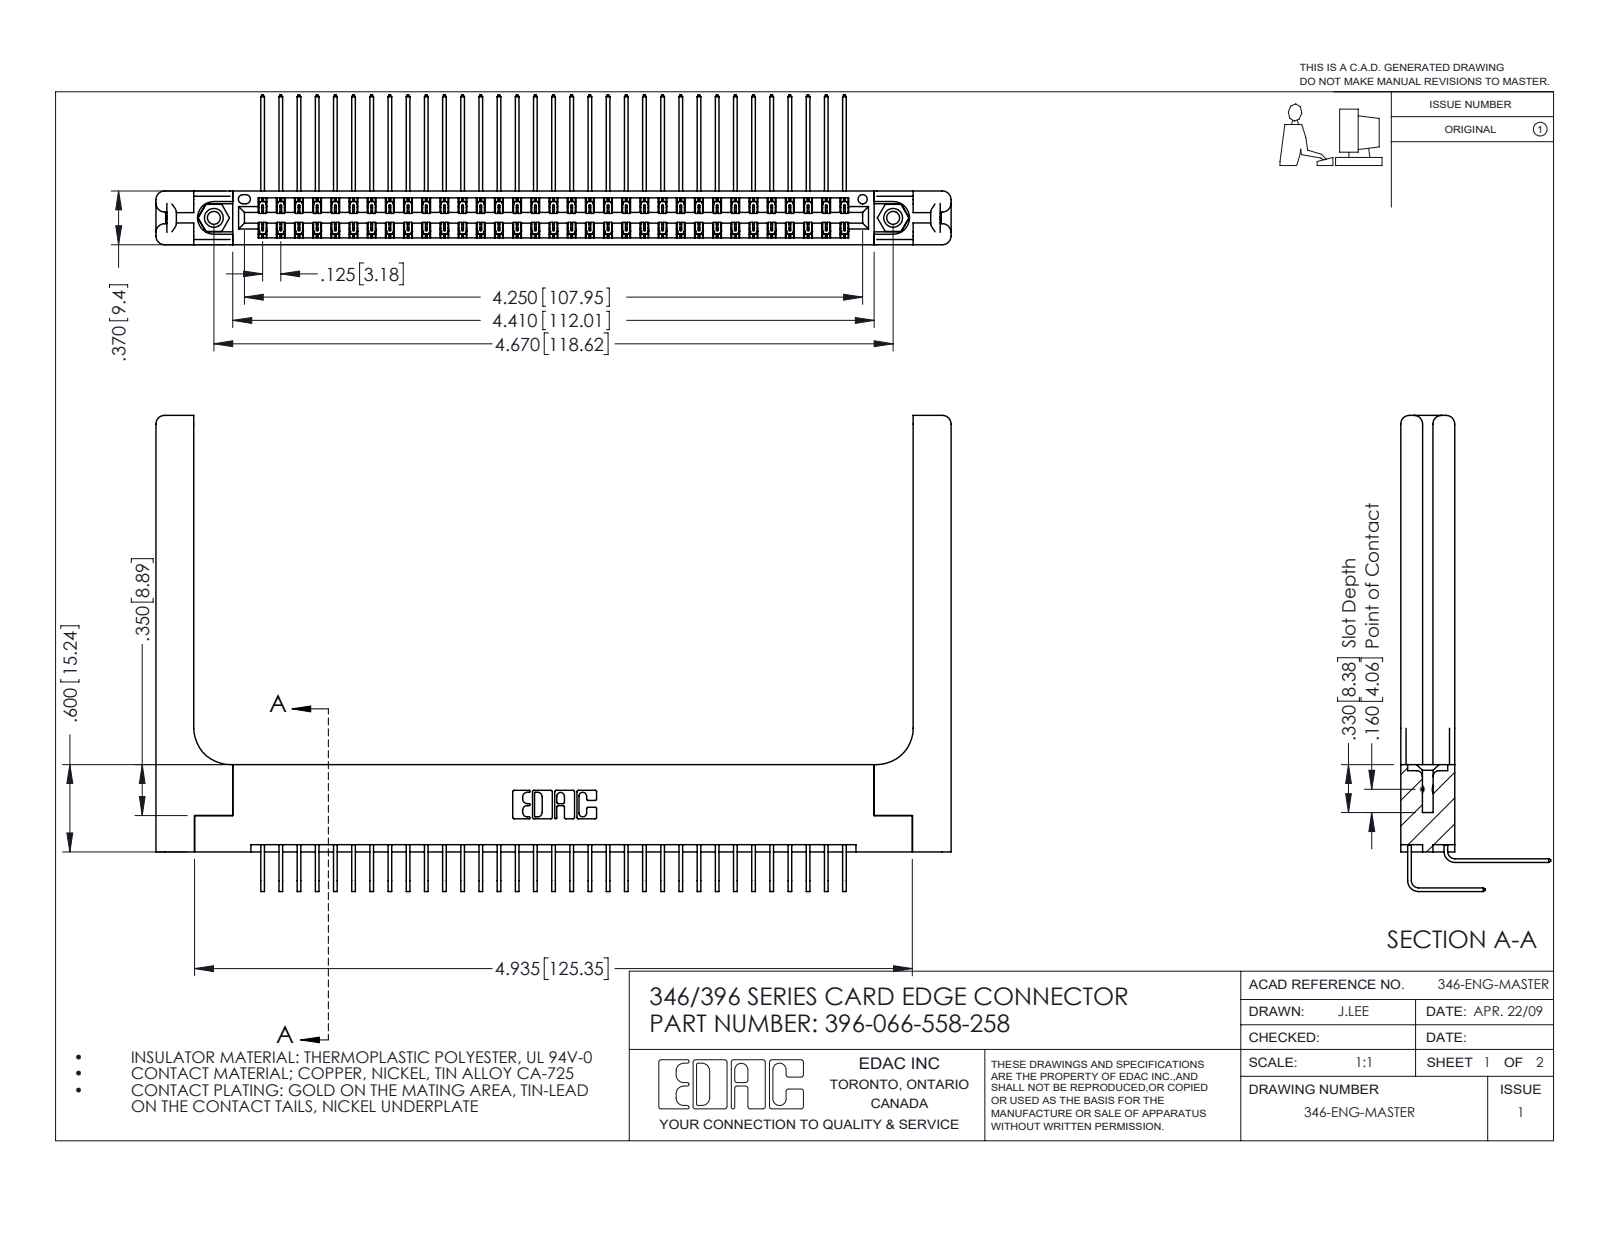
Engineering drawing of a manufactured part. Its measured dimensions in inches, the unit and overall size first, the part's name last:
Units: inches
Overall size (bounding box): 5.466 × 3.273 × 1.03
Round holes (diameter × count): ⌀0.089 ×2, ⌀0.125 ×2, ⌀0.156 ×2, ⌀0.064 ×1
Round bosses / shafts (diameter × count): ⌀0.155 ×2
Partial cylindrical surfaces — rounded edges, fillets, slot ends (radius × count): R0.006 ×99, R0.01 ×22, R0.06 ×16, R0.007 ×6, R0.031 ×6, R0.026 ×3, R0.014 ×2, R0.022 ×2
Main face-to-face distances: 0.322, 0.048, 0.37, 0.072, 0.025, 0.298, 0.148, 0.15, 0.25, 0.275
Hole centre spacings: 0.246, 4.462, 4.67
Volume: 1.302 in³ · Surface area: 39.83 in²
Bodies: 71 solids, 3942 faces (2666 planar, 1216 cylindrical, 60 other)
Part name (STEP PRODUCT): 346-220-058_345-220-058; 345-250-001_345-250-001-102; 396-066-558-258; 346 Part_Flush Mounting Lugs - 0.156 Dia-TH (+2 more)
STEP written by: SolidWorks 2016 (CONFIG_CONTROL_DESIGN)
